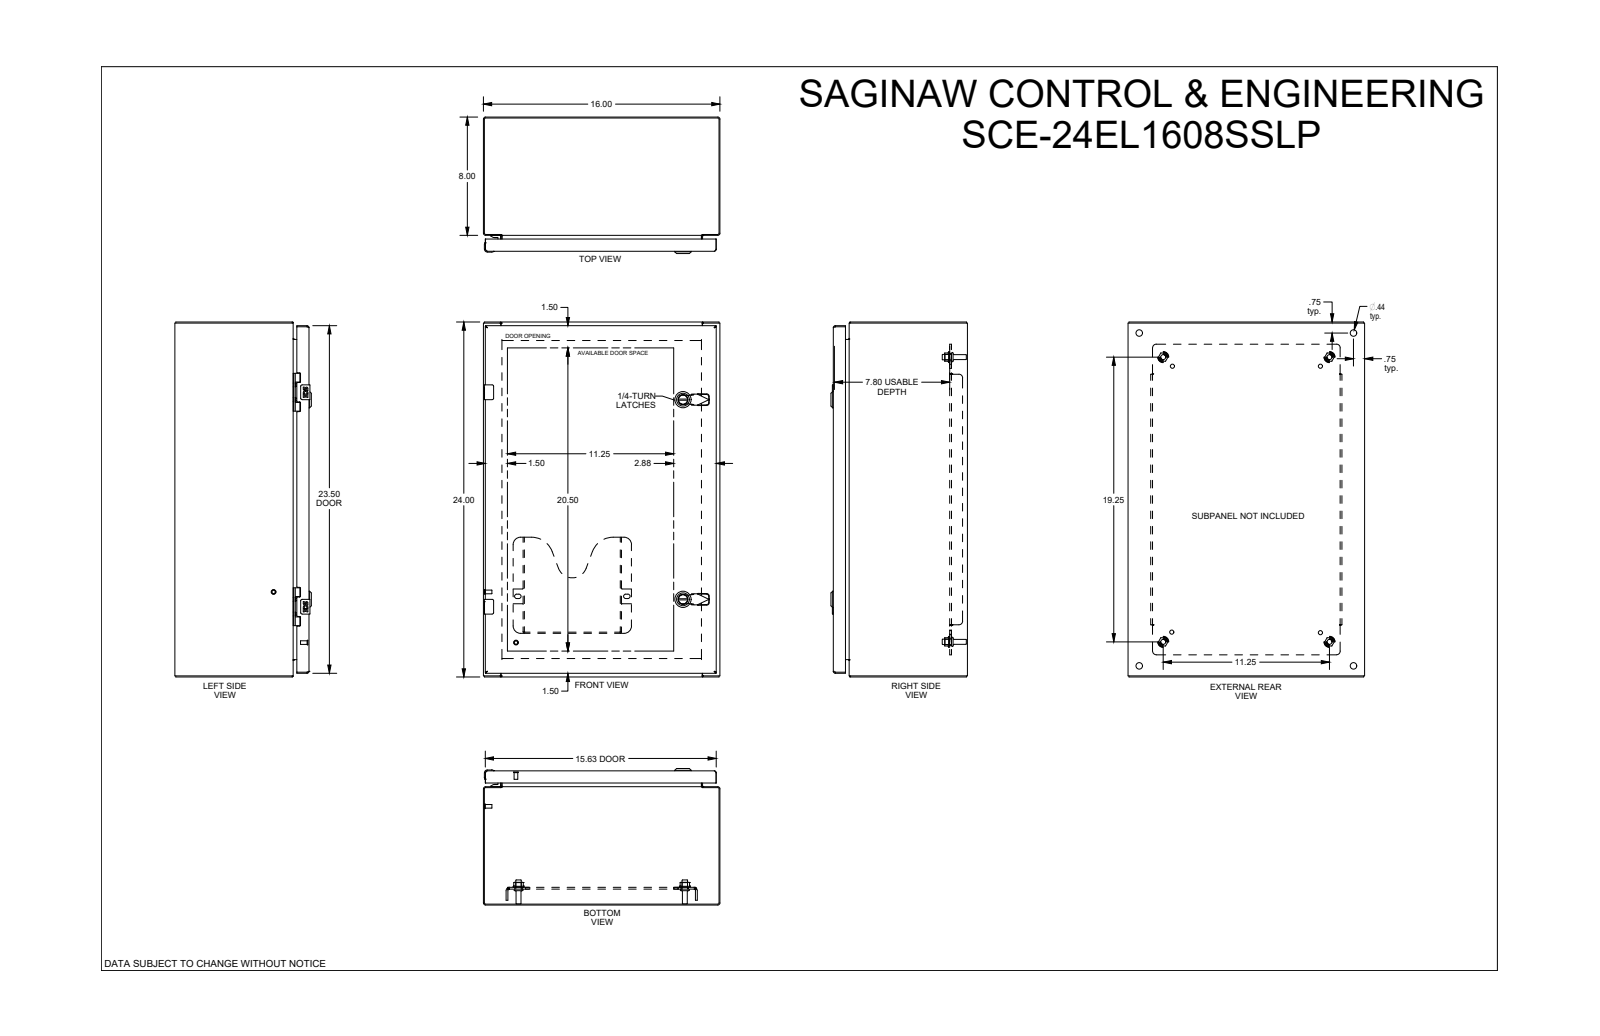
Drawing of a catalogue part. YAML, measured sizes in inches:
part_name: "SCE-24EL1608SSLP"
step_written_by: "SolidWorks 2019 (CONFIG_CONTROL_DESIGN)"
units: inches
bodies: {solids: 0, faces: 2806, planar: 1297, cylindrical: 749, other: 760}
overall_size: [24, 16, 9.23]
round_holes:
  - {diameter: 0.172, count: 4}
  - {diameter: 0.205, count: 4}
  - {diameter: 0.244, count: 4}
  - {diameter: 0.266, count: 4}
  - {diameter: 0.281, count: 4}
  - {diameter: 0.367, count: 4}
  - {diameter: 0.375, count: 4}
  - {diameter: 0.437, count: 4}
  - {diameter: 0.5, count: 4}
  - {diameter: 0.156, count: 2}
  - {diameter: 0.197, count: 2}
  - {diameter: 0.218, count: 2}
round_bosses_or_shafts:
  - {diameter: 0.17, count: 6}
  - {diameter: 0.366, count: 4}
  - {diameter: 0.332, count: 4}
  - {diameter: 0.25, count: 4}
  - {diameter: 0.248, count: 4}
  - {diameter: 0.196, count: 3}
  - {diameter: 1.102, count: 2}
  - {diameter: 0.866, count: 2}
partial_cylinders:
  - {radius: 0.012, count: 56}
  - {radius: 0.015, count: 32}
  - {radius: 0.01, count: 28}
  - {radius: 0.04, count: 23}
  - {radius: 0.02, count: 20}
  - {radius: 0.029, count: 12}
  - {radius: 0.07, count: 10}
  - {radius: 0.145, count: 10}
face_to_face_distances: [0.075, 0.075, 8.923, 8.998, 15.925, 9.073, 8.998, 1, 0.125, 1.125]
hole_center_spacings: [14.5, 0.985, 0.02, 2.298, 4.493, 12.978, 20.938, 24.526]
